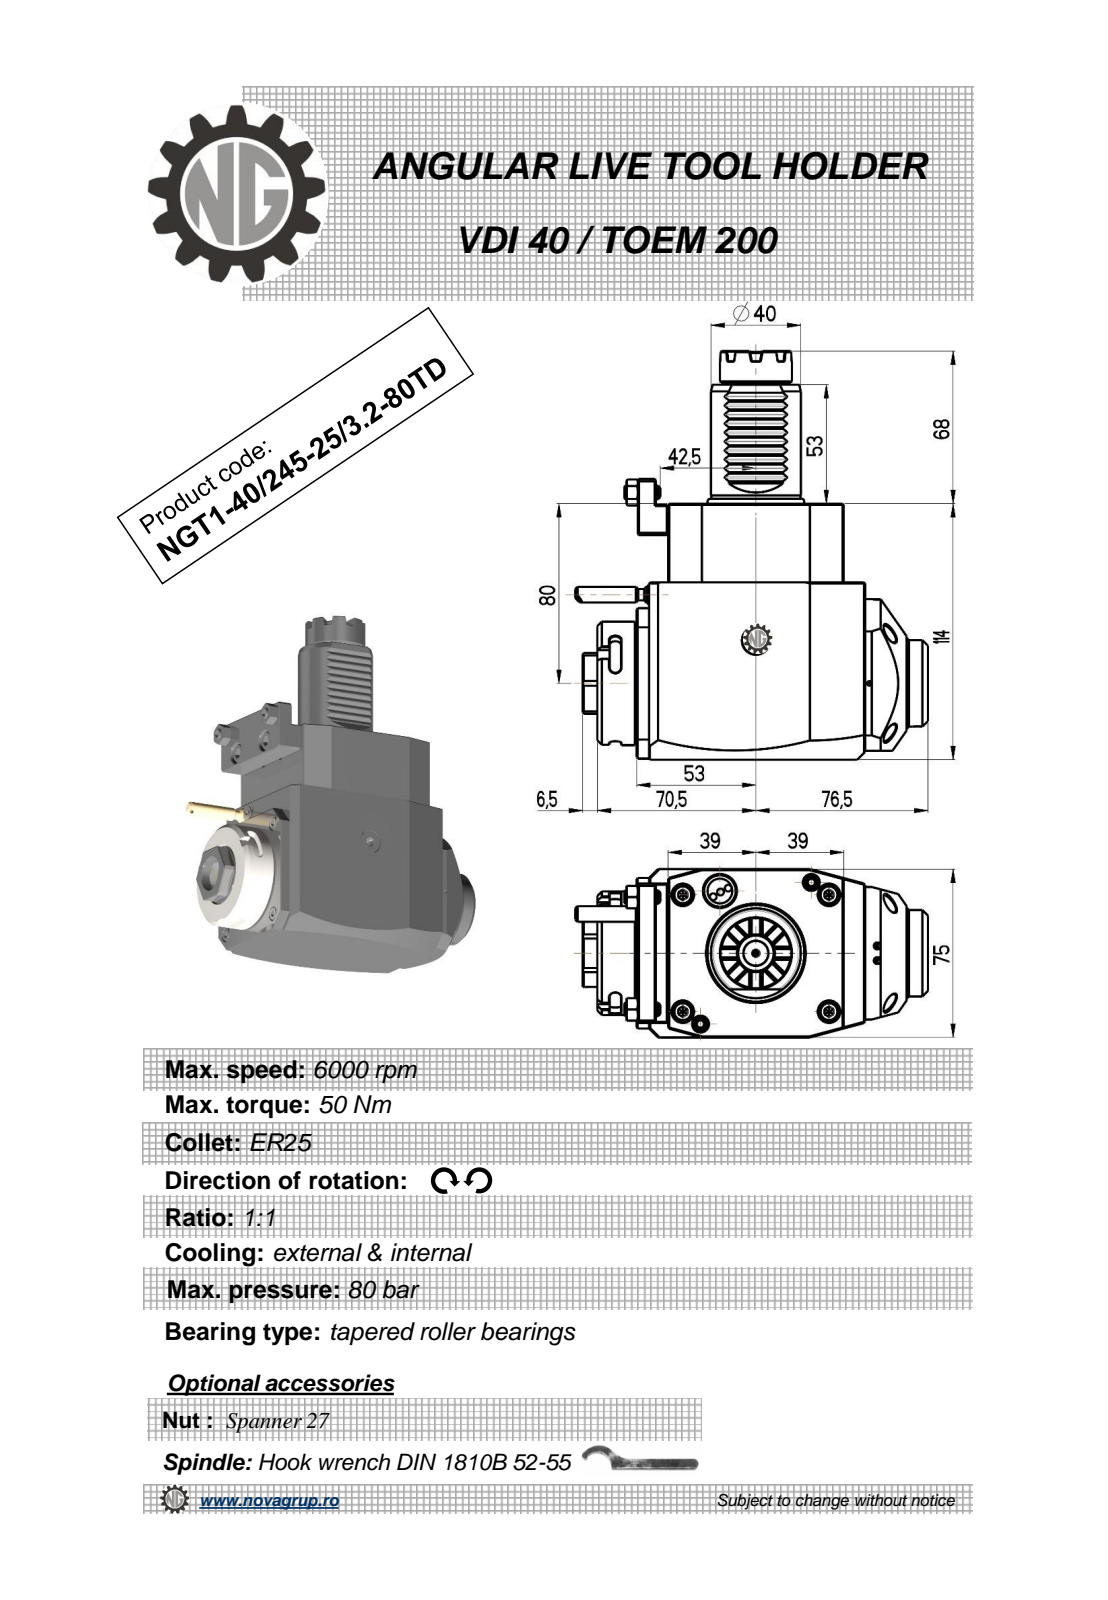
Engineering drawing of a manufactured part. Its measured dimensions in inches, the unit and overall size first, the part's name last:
Units: inches
Overall size (bounding box): 7.165 × 6.174 × 2.953
Round holes (diameter × count): ⌀0.098 ×1, ⌀0.118 ×1, ⌀0.709 ×1
Round bosses / shafts (diameter × count): ⌀0.236 ×2, ⌀2.165 ×1, ⌀1.89 ×1, ⌀1.575 ×1, ⌀1.516 ×1, ⌀1.26 ×1, ⌀0.677 ×1, ⌀0.315 ×1
Partial cylindrical surfaces — rounded edges, fillets, slot ends (radius × count): R0.012 ×10, R0.012 ×10, R0.098 ×6, R7.087 ×2, R0.02 ×1, R0.591 ×1, R0.965 ×1, R1.476 ×1
Main face-to-face distances: 2.953, 4.488, 0.02, 0.551, 3.622, 0.689, 4.311, 0.531, 0.217, 1.24
Hole centre spacings: 1.701
Volume: 59.48 in³ · Surface area: 113.8 in²
Bodies: 1 solid, 425 faces (219 planar, 74 cylindrical, 132 other)
Part name (STEP PRODUCT): NGT1_40_245_25_3_2_80TD
STEP written by: PRO/ENGINEER BY PARAMETRIC TECHNOLOGY CORPORATION, 2010280 (CONFIG_CONTROL_DESIGN)
